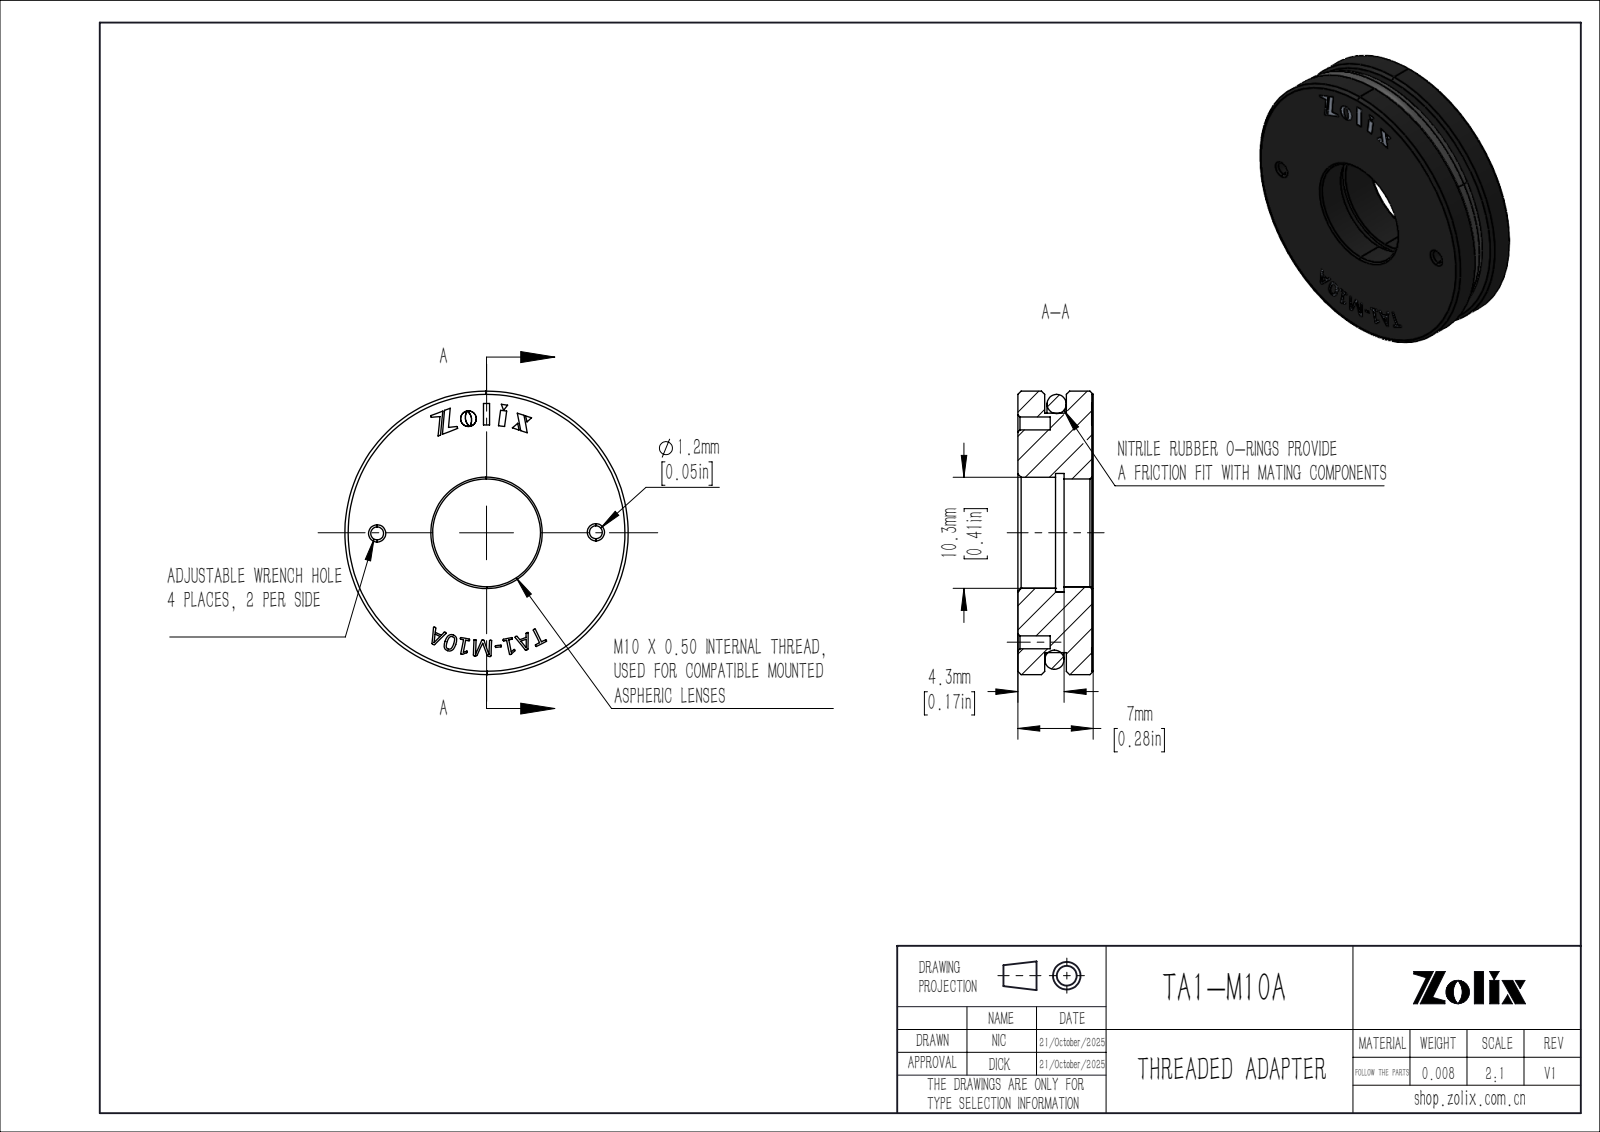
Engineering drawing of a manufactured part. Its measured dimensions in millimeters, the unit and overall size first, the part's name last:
Units: millimetres
Overall size (bounding box): 26.29 × 26.29 × 7
Round holes (diameter × count): ⌀1.2 ×4, ⌀10 ×1, ⌀10.3 ×1, ⌀11 ×1, ⌀25.69 ×1
Round bosses / shafts (diameter × count): ⌀26.29 ×1, ⌀22.2 ×1
Main face-to-face distances: 6.87, 2, 2.37, 4.5, 4.37, 2.5, 1, 2.57, 1.8, 4.3
Hole centre spacings: 10.15, 14.35, 20.3
Volume: 3 006 mm³ · Surface area: 2 443 mm²
Bodies: 2 solids, 337 faces (226 planar, 22 cylindrical, 89 other)
Part name (STEP PRODUCT): TA1-M10A
STEP written by: SolidWorks 2020 (CONFIG_CONTROL_DESIGN)
